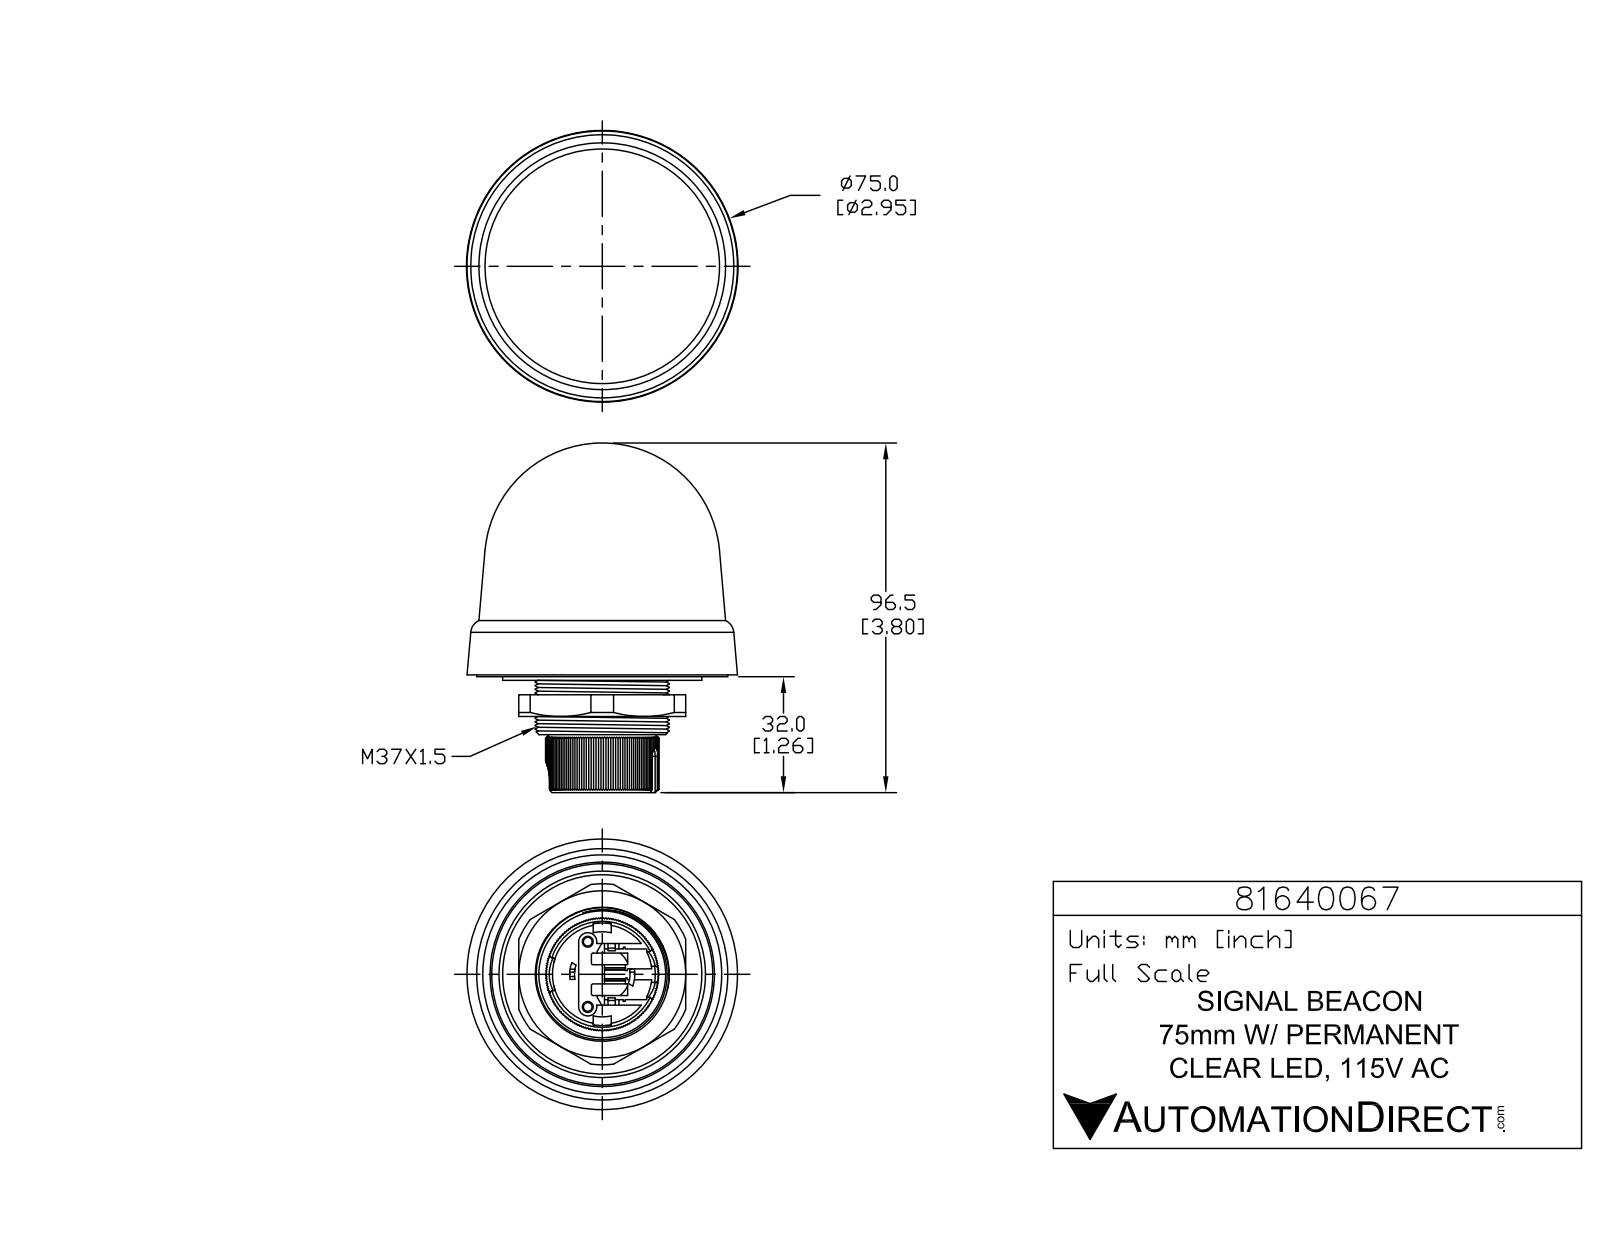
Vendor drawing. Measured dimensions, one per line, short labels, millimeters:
name: 81640067
written by: SolidWorks 2019 (CONFIG_CONTROL_DESIGN)
unit: mm
bodies: 3 solids, 560 faces (432 planar, 80 cylindrical, 48 other)
size: 96.5 × 74.7 × 74.7
volume: 202 500 mm³; area: 37 860 mm²
holes: 2× ⌀2.4, 2× ⌀3, 1× ⌀15.3, 1× ⌀29
bosses: 2× ⌀5.5, 2× ⌀1.7, 1× ⌀55, 1× ⌀37, 1× ⌀23.5
rounds: 6× R0.2, 6× R1, 4× R0.5, 2× R0.8, 2× R2, 2× R2.5, 1× R4.5, 1× R9
face distances: 4.5, 9, 5, 11, 13, 8.5, 1.5, 10, 3, 4
hole spacings: 9.9, 18
